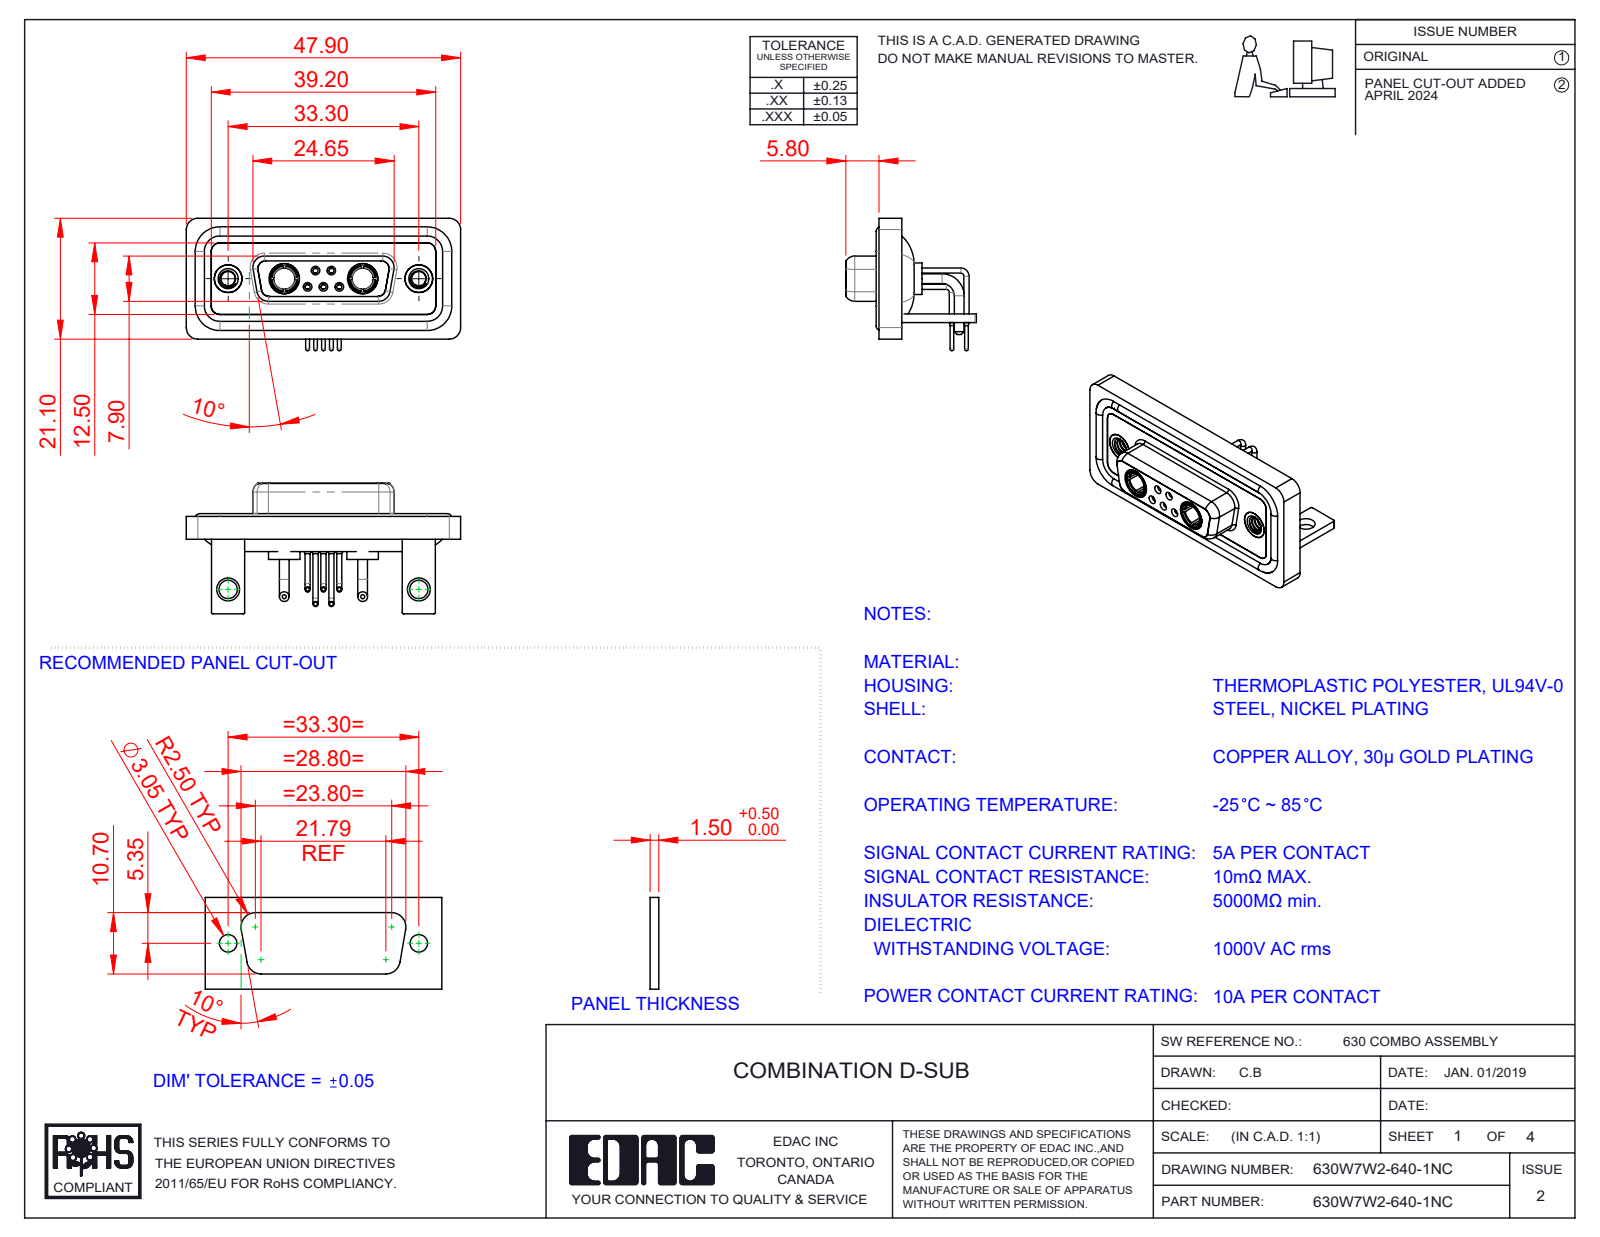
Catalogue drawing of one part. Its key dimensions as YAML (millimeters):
part_name: "630Combo Shell Front_15 Contacts; 630Combo Housing_7W2; 630Combo Contact Row 1_50 Contacts; 630Combo Threaded Rivet_A (+6 more)"
step_written_by: "SolidWorks 2023 (CONFIG_CONTROL_DESIGN)"
units: millimeters
bodies: {solids: 18, faces: 849, planar: 258, cylindrical: 375, other: 216}
overall_size: [47.9, 23.12, 22.8]
volume: 6440
surface_area: 10843
round_holes:
  - {diameter: 0.9, count: 5}
  - {diameter: 1.1, count: 5}
  - {diameter: 1.5, count: 5}
  - {diameter: 2, count: 5}
  - {diameter: 4.85, count: 4}
  - {diameter: 1.6, count: 3}
  - {diameter: 1.7, count: 2}
  - {diameter: 2.5, count: 2}
  - {diameter: 3.2, count: 2}
  - {diameter: 3.7, count: 2}
  - {diameter: 4, count: 2}
  - {diameter: 4.05, count: 2}
round_bosses_or_shafts:
  - {diameter: 1.6, count: 6}
  - {diameter: 0.9, count: 5}
  - {diameter: 0.65, count: 5}
  - {diameter: 1.7, count: 4}
  - {diameter: 5.5, count: 2}
  - {diameter: 5.2, count: 2}
  - {diameter: 4.96, count: 2}
  - {diameter: 4.95, count: 2}
partial_cylinders:
  - {radius: 2, count: 21}
  - {radius: 1.5, count: 18}
  - {radius: 0.25, count: 16}
  - {radius: 1.35, count: 12}
  - {radius: 1.6, count: 8}
  - {radius: 0.5, count: 5}
  - {radius: 0.6, count: 4}
  - {radius: 0.65, count: 4}
face_to_face_distances: [0.4, 2.9, 1.5, 1.8, 3.7, 1.1, 4.1, 1.6, 2.5, 1.4]
hole_center_spacings: [3.16, 2.77, 9.8, 23.5, 33.3, 4.31, 4.33, 5.03]
